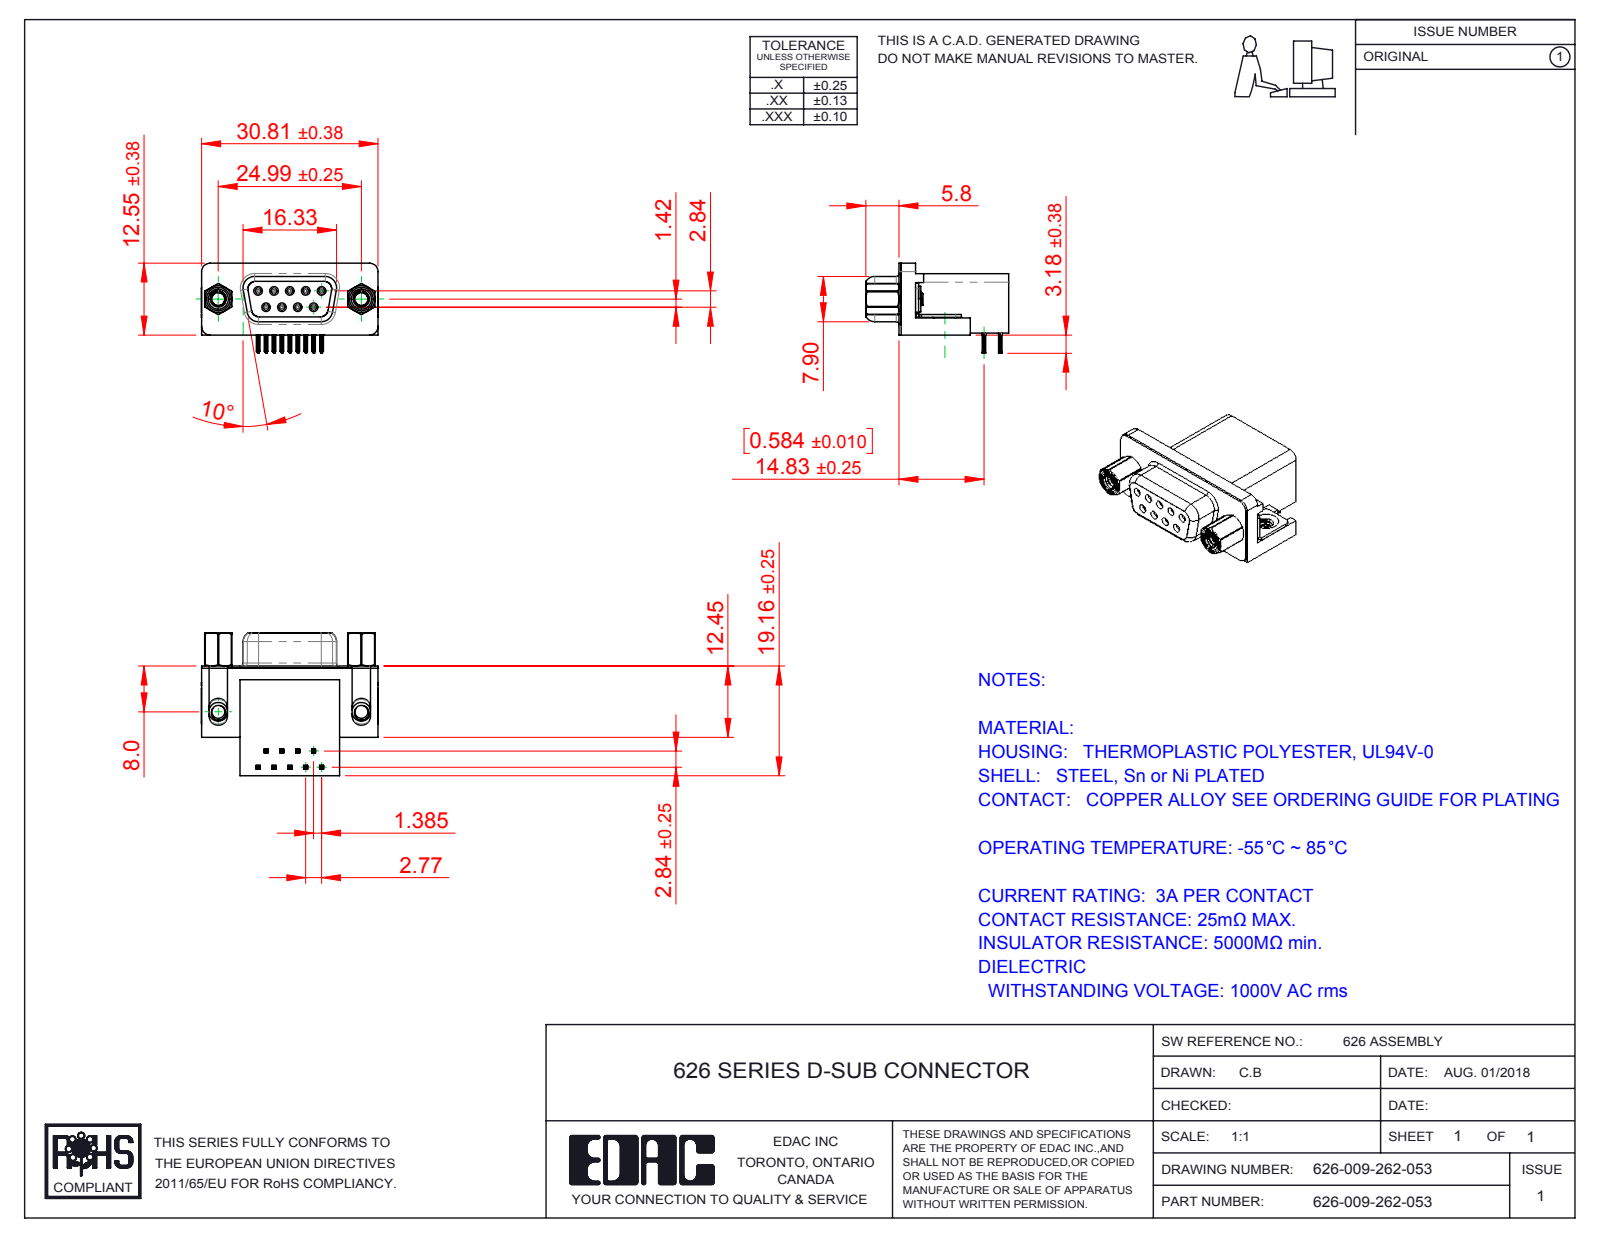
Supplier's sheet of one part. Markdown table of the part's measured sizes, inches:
| quantity | value |
| --- | --- |
| part name | 626 Housing_9 Socket; 626 4-40 Hex Standoff 5; 626 Shell_9 Socket; 626 Contact Bottom (+4 more) |
| STEP written by | SolidWorks 2016 (CONFIG_CONTROL_DESIGN) |
| units | inches |
| bodies | 17 solids, 1724 faces (700 planar, 508 cylindrical, 516 other) |
| overall size | 1.216 × 0.983 × 0.619 |
| volume | 0.322 in³ |
| surface area | 10.16 in² |
| round holes (diameter × count) | 0.031 × 9, 0.035 × 9, 0.089 × 2, 0.09 × 2, 0.091 × 2, 0.122 × 2, 0.157 × 2, 0.189 × 2, 0.197 × 2 |
| round bosses / shafts (diameter × count) | 0.047 × 9, 0.193 × 2, 0.185 × 2, 0.177 × 2, 0.152 × 2, 0.128 × 2, 0.11 × 2 |
| partial cylindrical surfaces (radius × count) | 0.004 × 72, 0.006 × 36, 0.014 × 18, 0.039 × 18, 0.013 × 9, 0.053 × 8, 0.063 × 8, 0.059 × 7 |
| main face-to-face distances | 0.016, 0.407, 0.014, 0.739, 0.754, 0.64, 0.244, 0.114, 0.098, 0.228 |
| hole center spacings | 0.124, 0.109, 0.218, 0.198, 0.198, 0.327, 0.294, 0.295 |
